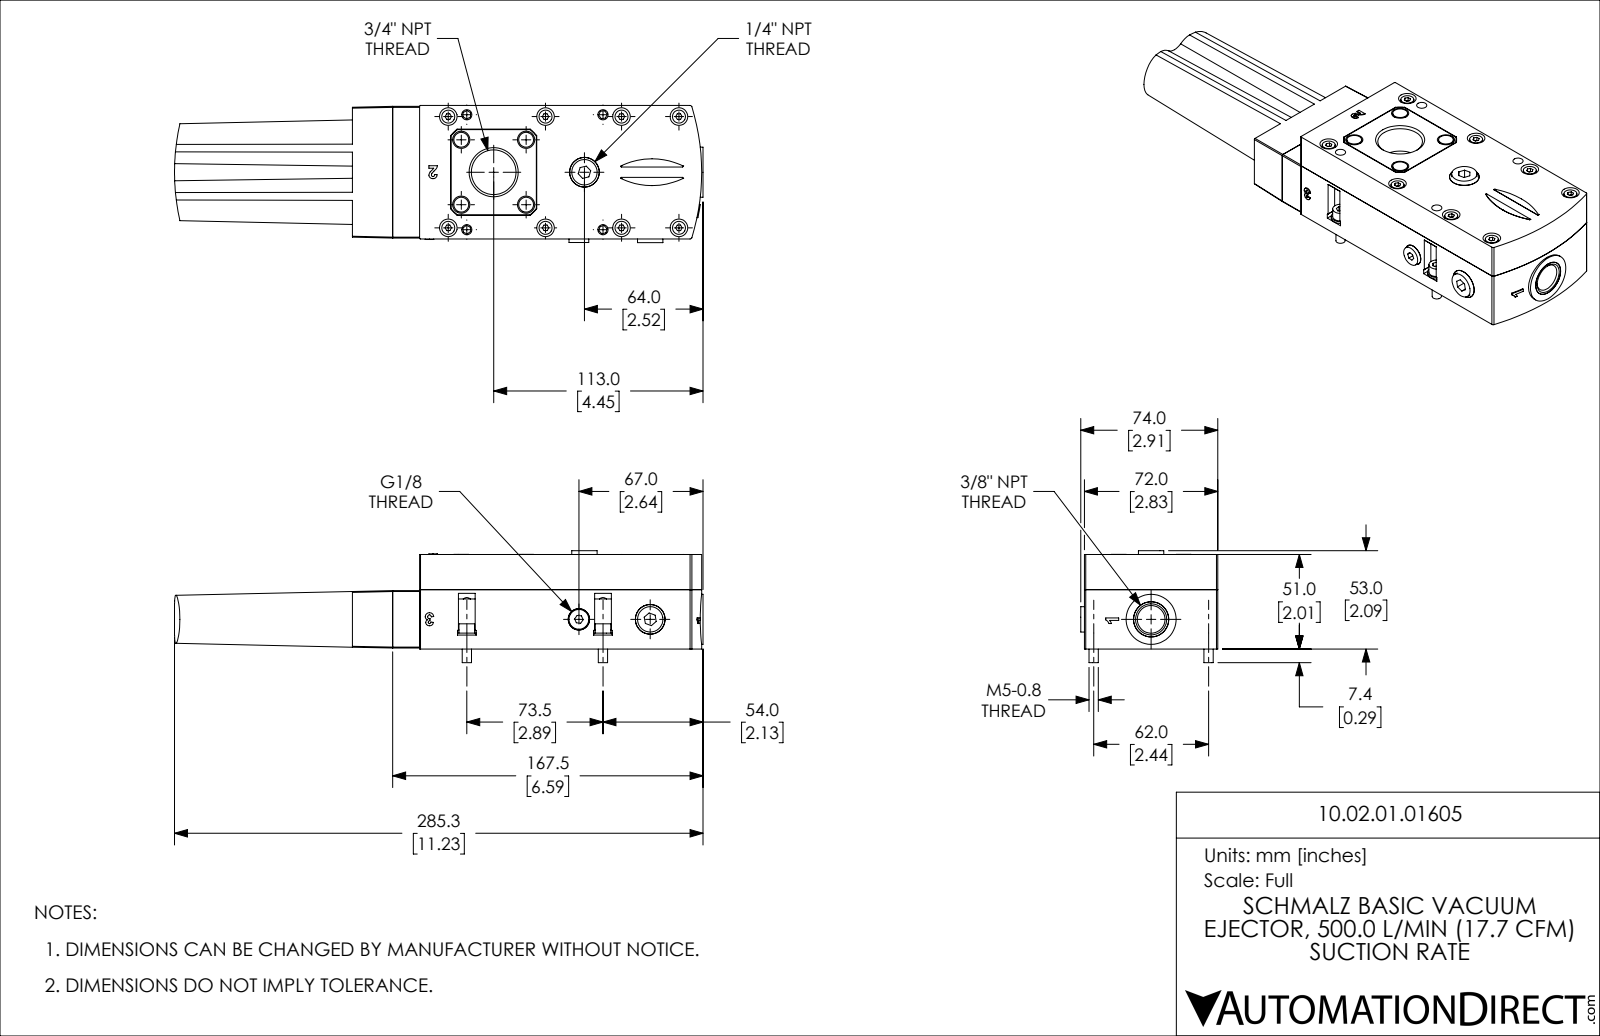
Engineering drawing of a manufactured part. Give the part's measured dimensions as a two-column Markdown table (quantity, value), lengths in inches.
| quantity | value |
| --- | --- |
| part name | 10.02.01.01605 |
| STEP written by | SolidWorks 2021 (CONFIG_CONTROL_DESIGN) |
| units | inches |
| bodies | 43 solids, 899 faces (413 planar, 394 cylindrical, 92 other) |
| overall size | 11.23 × 2.913 × 2.378 |
| volume | 43.95 in³ |
| surface area | 223.8 in² |
| round holes (diameter × count) | 0.177 × 12, 0.374 × 9, 0.13 × 8, 0.244 × 8, 0.256 × 8, 0.138 × 4, 0.169 × 4, 0.209 × 4, 0.217 × 4, 0.453 × 3, 0.173 × 2, 0.315 × 2 |
| round bosses / shafts (diameter × count) | 0.276 × 10, 0.157 × 10, 0.236 × 8, 0.394 × 4, 0.335 × 4, 0.315 × 4, 0.197 × 4, 0.111 × 4 |
| partial cylindrical surfaces (radius × count) | 0.02 × 14, 0.181 × 8, 0.177 × 4, 0.199 × 4, 0.039 × 2, 0.373 × 2, 4.724 × 2, 0.344 × 1 |
| main face-to-face distances | 1.26, 0.748, 2.008, 2.835, 0.571, 0.02, 1.24, 0.157, 1.248, 1.996 |
| hole center spacings | 1.371, 1.364, 0.396, 0.964, 0.974, 1.33, 1.378, 1.939 |
